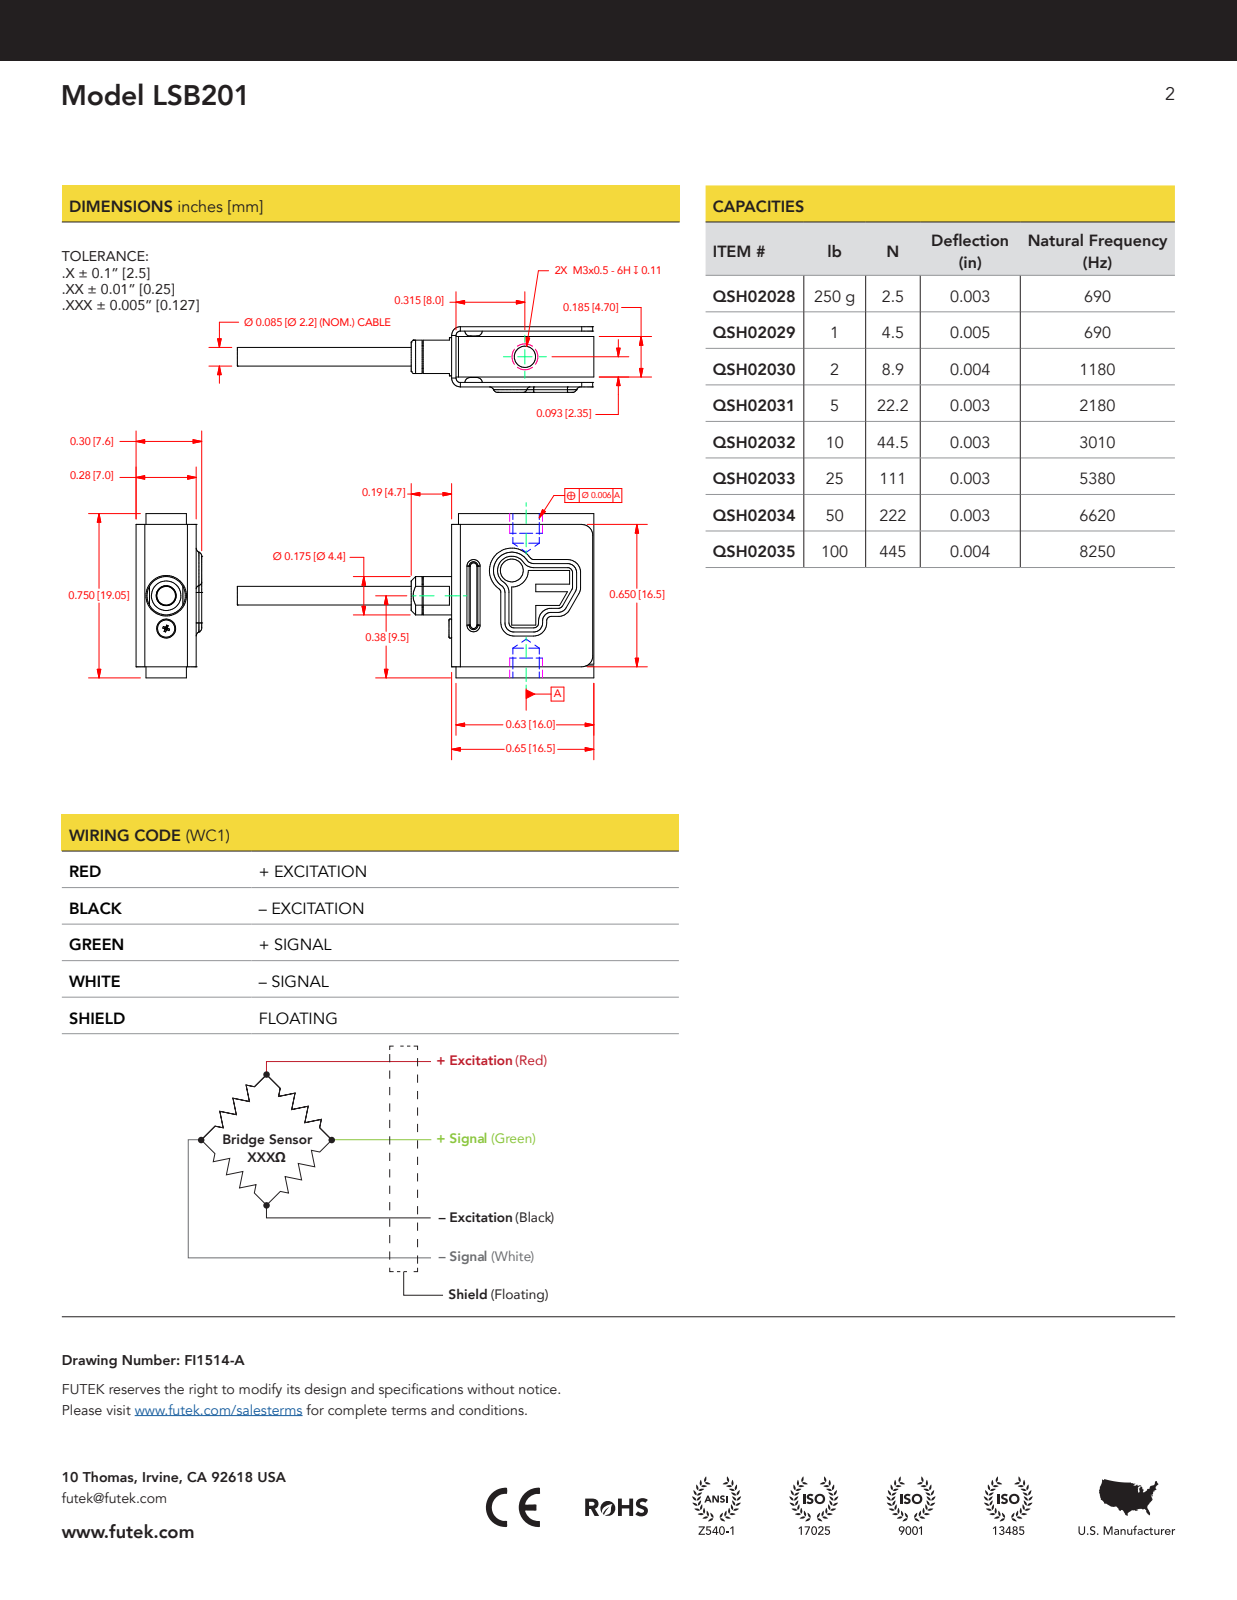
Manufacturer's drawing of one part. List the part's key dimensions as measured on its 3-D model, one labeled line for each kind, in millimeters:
Part name (STEP PRODUCT): Assembly2_Shrinkwrap_1
STEP written by: Autodesk Inventor 2018 (AUTOMOTIVE_DESIGN)
Units: millimetres
Bodies: 1 solid, 522 faces (311 planar, 76 cylindrical, 135 other)
Overall size (bounding box): 139.2 × 19.1 × 7.6
Volume: 2 210 mm³ · Surface area: 3 230 mm²
Round holes (diameter × count): ⌀0.9 ×1, ⌀1.4 ×1, ⌀2.3 ×1, ⌀2.3 ×1, ⌀2.5 ×1, ⌀2.5 ×1, ⌀2.6 ×1, ⌀3 ×1, ⌀4.7 ×1
Round bosses / shafts (diameter × count): ⌀4.4 ×1, ⌀2.7 ×1, ⌀2.6 ×1, ⌀2.2 ×1, ⌀2.2 ×1, ⌀1.2 ×1, ⌀0.9 ×1
Partial cylindrical surfaces — rounded edges, fillets, slot ends (radius × count): R0.5 ×32, R0.1 ×4, R0.3 ×4, R0.6 ×4, R1 ×2, R1.3 ×2, R1.9 ×1
Main face-to-face distances: 1.1, 5.8, 4.7, 0.6, 0.5, 5.3, 6.5, 0.6, 6, 0.5
Hole centre spacings: 3.8, 3.8, 3.8
